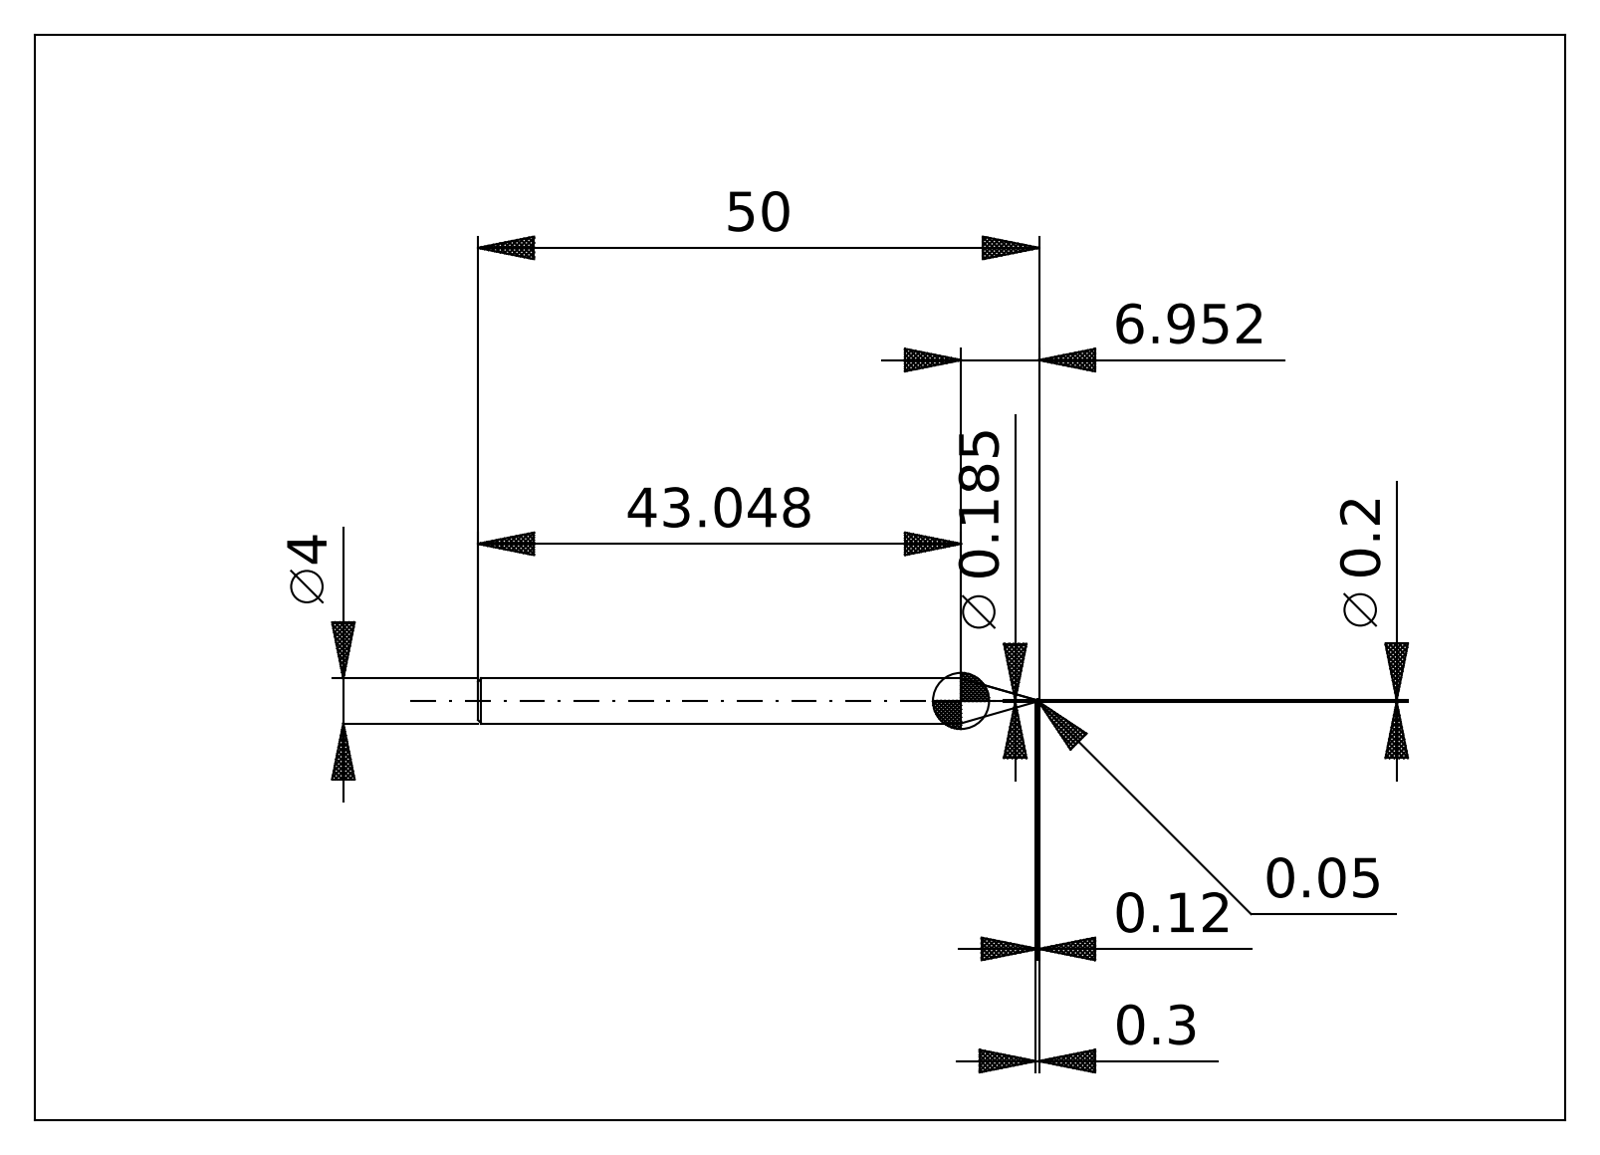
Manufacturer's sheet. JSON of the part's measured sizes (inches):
{"step_written_by": "ACIS (automotive_design)", "units": "inches", "bodies": {"solids": 2, "faces": 26, "planar": 6, "cylindrical": 8, "other": 12}, "overall_size": [1.969, 0.157, 0.157], "volume_in3": 0.035, "surface_area_in2": 0.925, "round_bosses_or_shafts": [[0.157, 1]], "face_to_face_distances": [1.967, 1.964, 1.969, 0.274, 0.272, 0.269, 1.695]}
